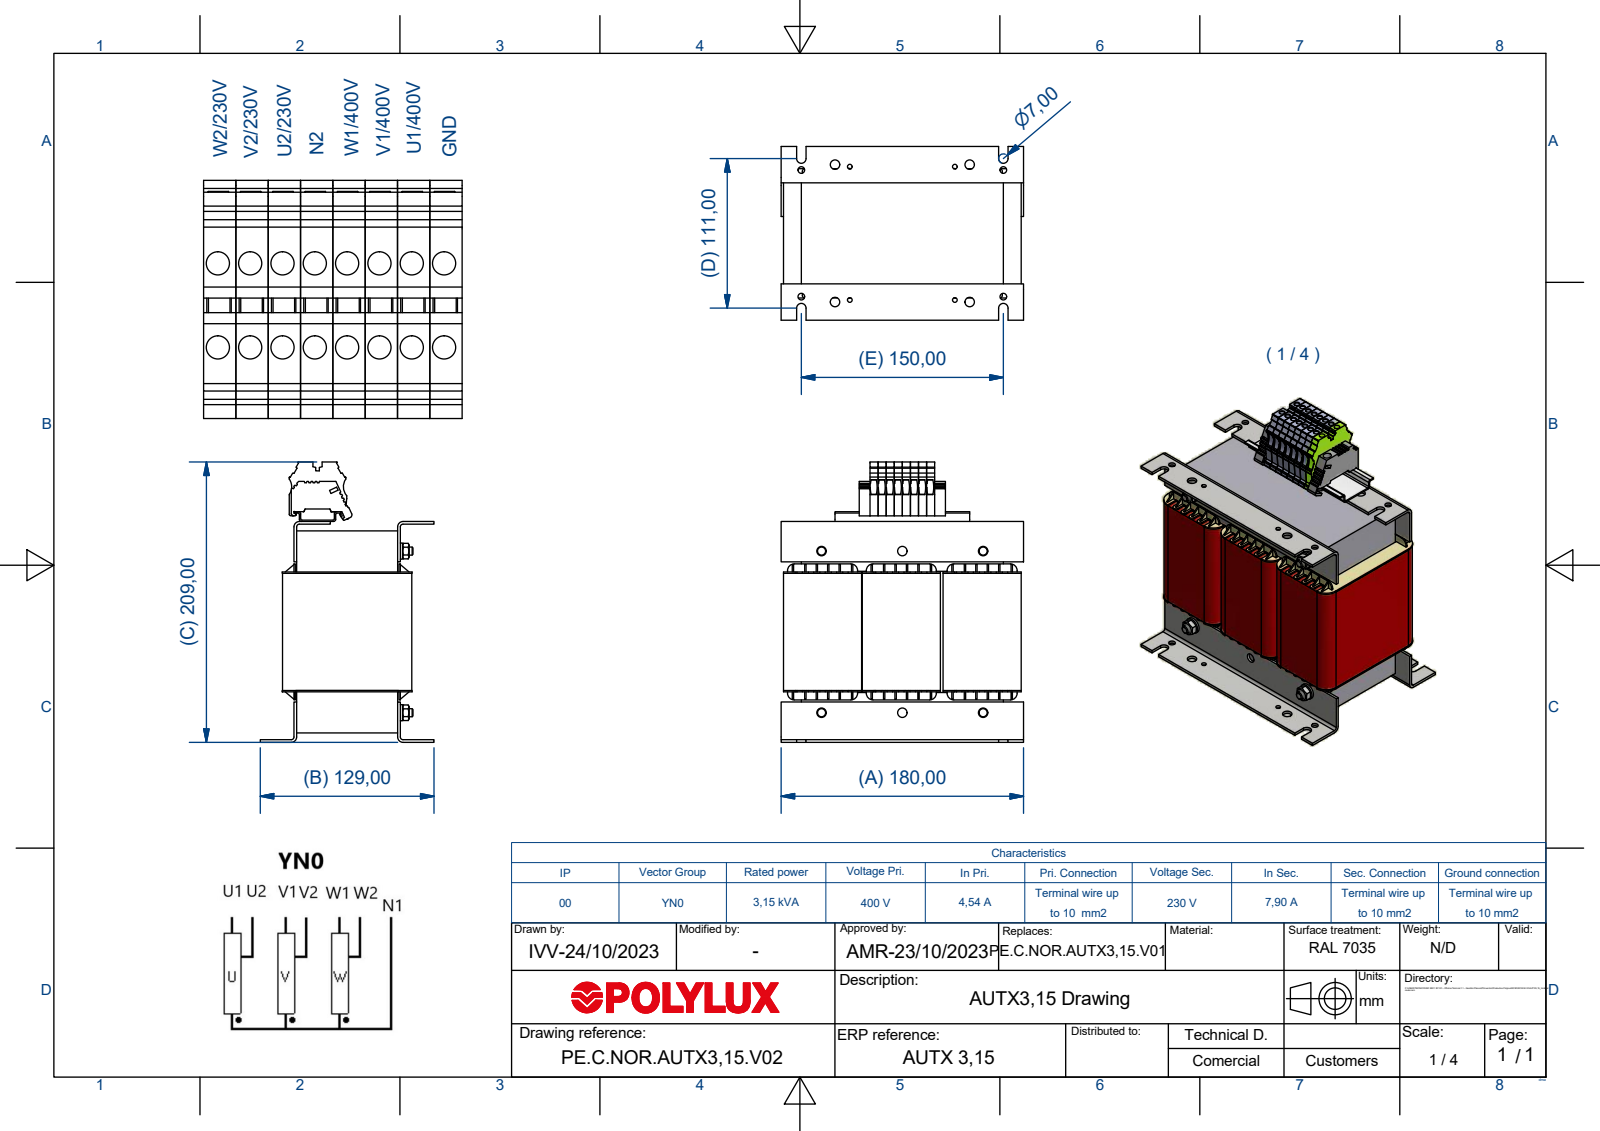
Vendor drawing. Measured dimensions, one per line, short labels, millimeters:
name: AUTX3,15_brida al revés; Núcleo 30x75 EIT; Carrete 30x75; bobina 30x75 (+8 more)
written by: Autodesk Inventor 2018 (AUTOMOTIVE_DESIGN)
unit: mm
bodies: 38 solids, 2453 faces (1700 planar, 729 cylindrical, 24 other)
size: 208.15 × 180 × 129
volume: 2 272 000 mm³; area: 582 092 mm²
holes: 16× ⌀4.3, 12× ⌀7, 6× ⌀3.5, 6× ⌀4.92, 4× ⌀3, 4× ⌀6, 4× ⌀6.65, 4× ⌀8.4, 2× ⌀5.8
bosses: 4× ⌀16, 4× ⌀8
rounds: 33× R0.5, 26× R10, 24× R2.25, 16× R24.01, 13× R0.1, 12× R0.3, 12× R1, 12× R5
face distances: 1.25, 118.5, 60, 32.75, 58.5, 1, 2, 31.5, 44.75, 34
hole spacings: 6, 16.71, 12, 19.68, 18, 23.82, 56, 15.6
